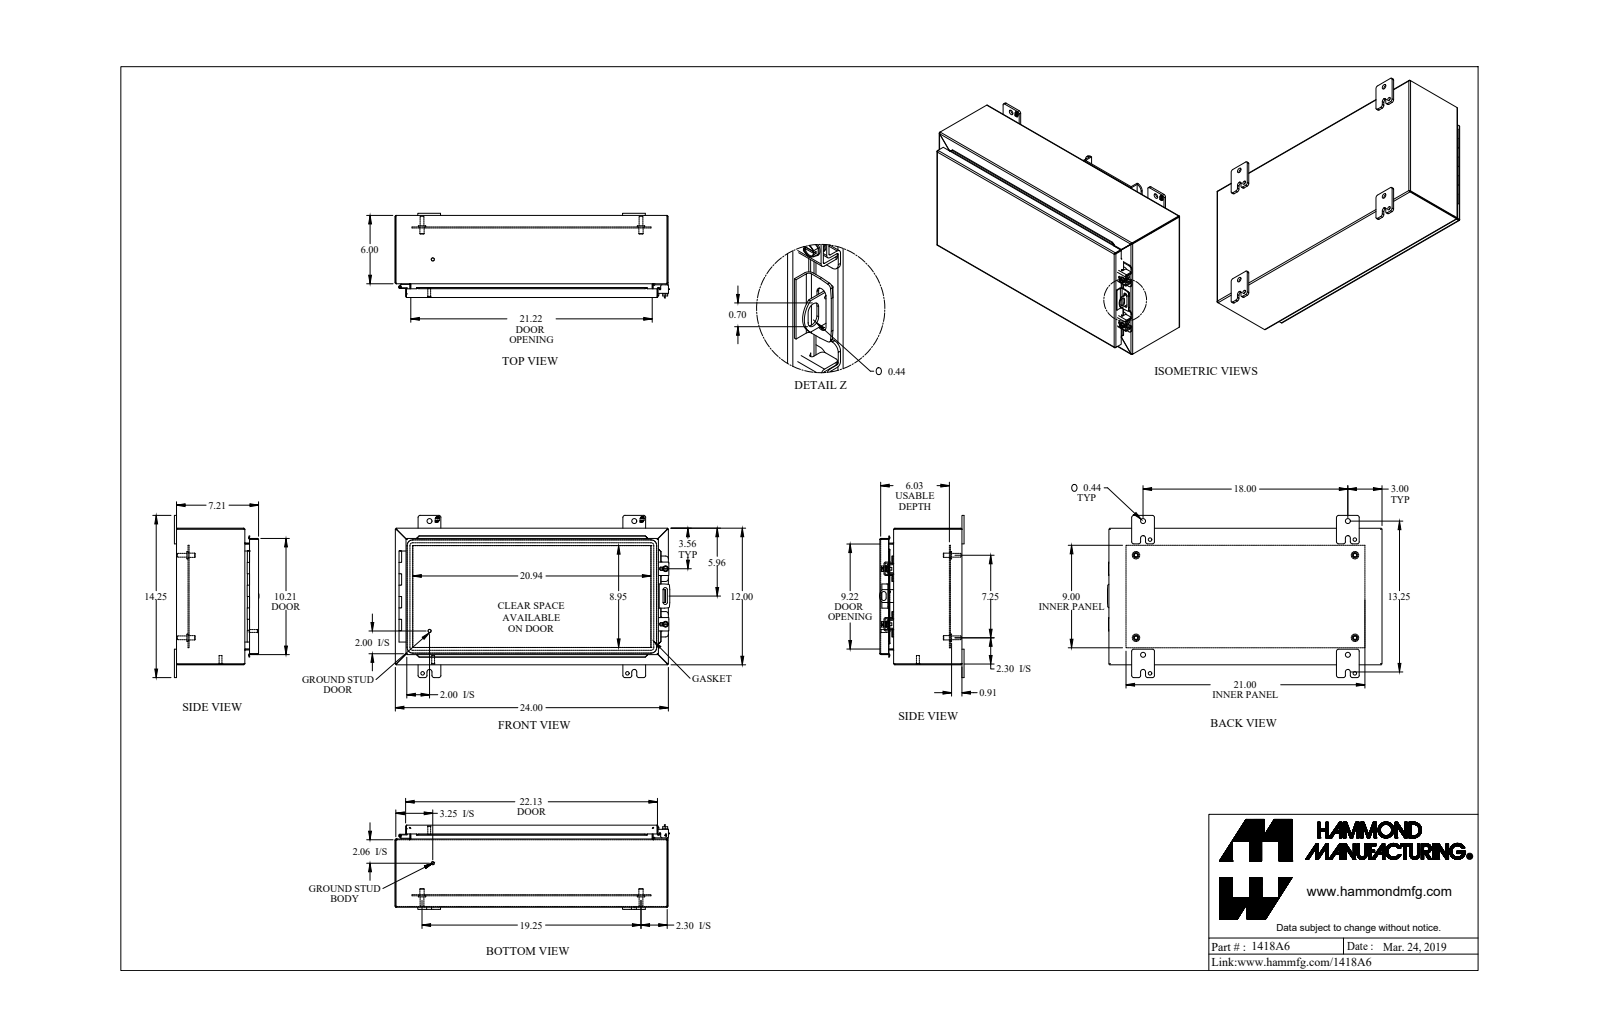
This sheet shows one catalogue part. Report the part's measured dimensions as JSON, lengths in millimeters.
{"part_name": "1418A6", "step_written_by": "SolidWorks 2019 (AUTOMOTIVE_DESIGN)", "units": "millimeters", "bodies": {"solids": 31, "faces": 984, "planar": 675, "cylindrical": 257, "other": 52}, "overall_size": [612.8, 362, 188.9], "volume_mm3": 1909000, "surface_area_mm2": 1937000, "round_holes": [[8, 4], [11.1, 4], [12.7, 4], [5.4, 2], [6.7, 2], [7.8, 2], [9.5, 2], [11.3, 2], [2.8, 1], [3.2, 1]], "round_bosses_or_shafts": [[16.5, 4], [9.5, 4], [8.4, 4], [25.4, 2], [12.7, 2], [9.9, 2], [7.1, 2], [6.4, 2]], "partial_cylinders_radius": [[4.8, 26], [0.9, 20], [2.7, 20], [1.2, 13], [3.6, 13], [0.2, 8], [1.1, 8], [2, 8]], "face_to_face_distances": [1.8, 180.7, 178.8, 303, 182.5, 23.8, 25.6, 2.4, 154.5, 152.6], "hole_center_spacings": [457.2, 522.5, 546, 61.8, 77.9, 184.2, 479.2, 522.5]}
